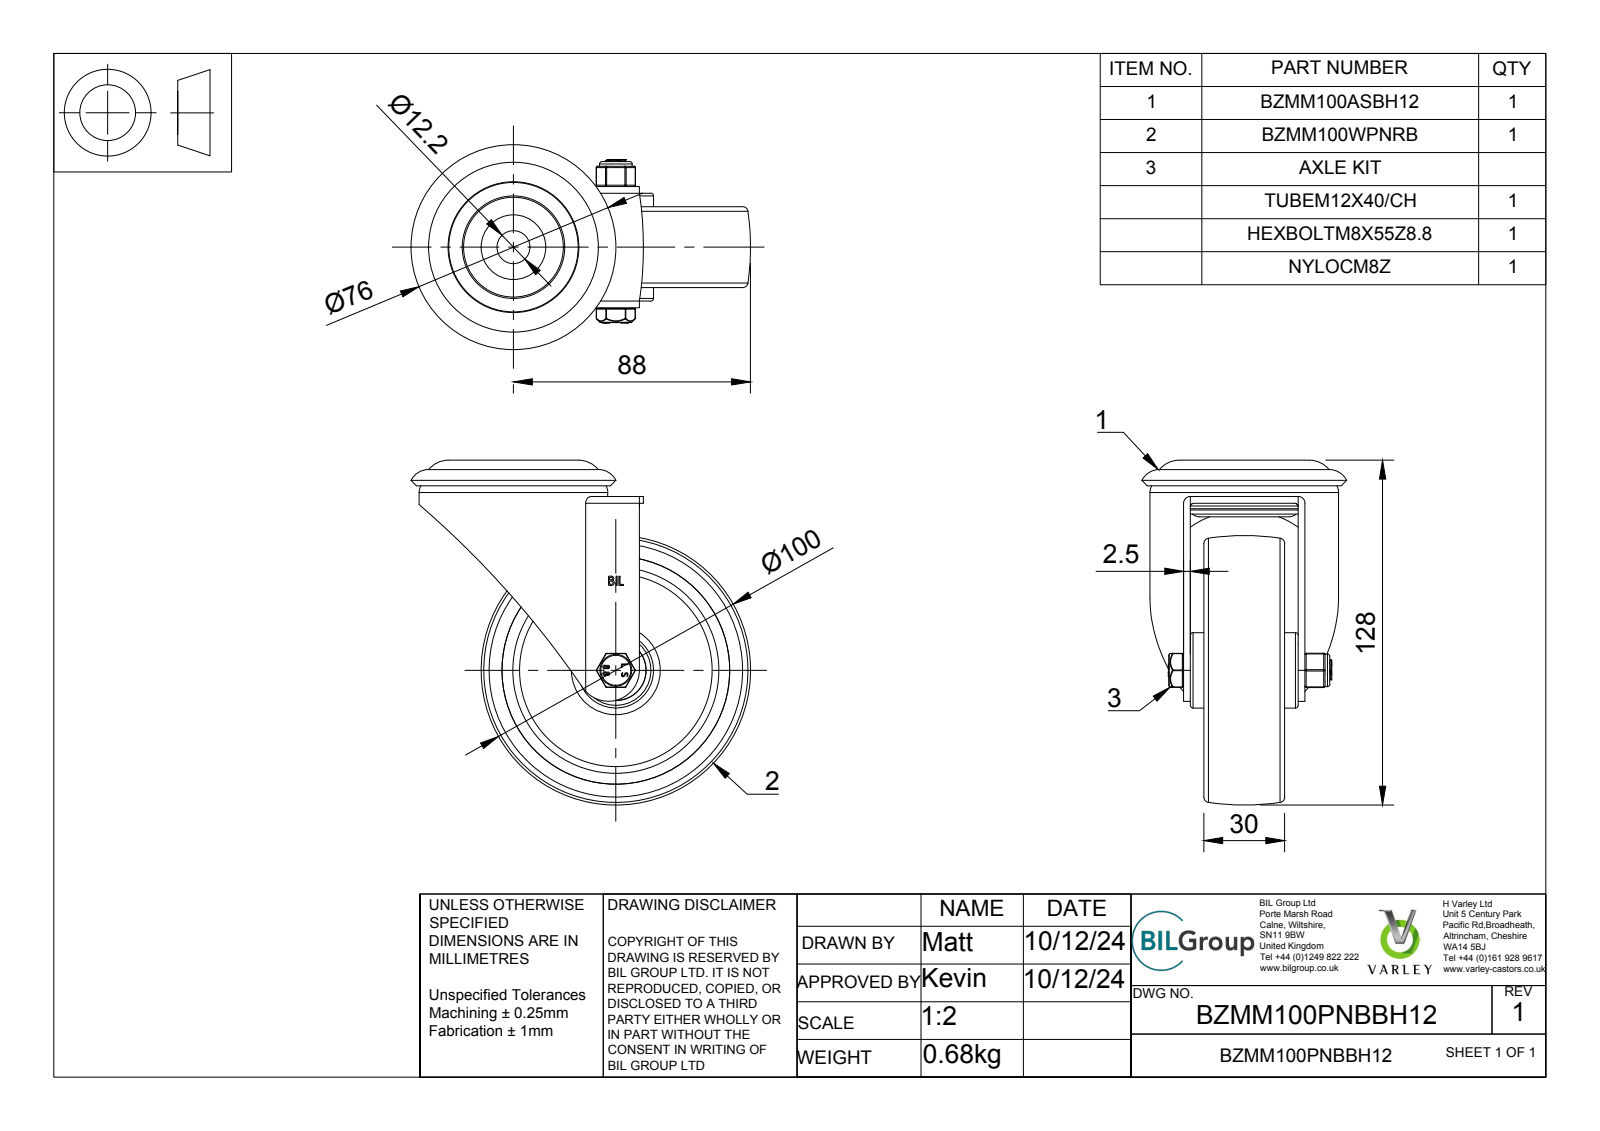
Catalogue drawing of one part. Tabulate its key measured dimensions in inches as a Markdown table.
| quantity | value |
| --- | --- |
| part name | BZMM100PNBBH12 v3; BZMM100ASBH12 v1; ZINC PLATED PRESSED STEEL HEAD; ZINC PLATED, PRESSED STEEL FORKS (+7 more) |
| STEP written by | Autodesk Translation Framework v13.20.0.188 (AP242_MANAGED_MODEL_BASED_3D_ENGINEERING_MIM_LF) |
| units | inches |
| bodies | 18 solids, 439 faces (180 planar, 158 cylindrical, 101 other) |
| overall size | 5.039 × 4.961 × 2.992 |
| volume | 11.52 in³ |
| surface area | 166.2 in² |
| round holes (diameter × count) | 0.026 × 2, 0.315 × 1, 0.323 × 1, 0.331 × 1, 0.339 × 1, 0.48 × 1, 0.492 × 1, 0.512 × 1, 0.807 × 1, 0.886 × 1, 2.559 × 1, 2.835 × 1 |
| round bosses / shafts (diameter × count) | 0.154 × 8, 2.756 × 1, 1.949 × 1, 1.496 × 1, 1.102 × 1, 0.945 × 1, 0.882 × 1, 0.839 × 1 |
| partial cylindrical surfaces (radius × count) | 0.02 × 18, 0.01 × 12, 0.013 × 4, 0.025 × 4, 0.049 × 4, 0.025 × 2, 0.025 × 2, 0.098 × 2 |
| main face-to-face distances | 0.098, 0.512, 0.669, 0.157, 0.197, 0.709, 0.866, 1.378, 1.673, 0.965 |
| hole center spacings | 0.127, 0.098 |
